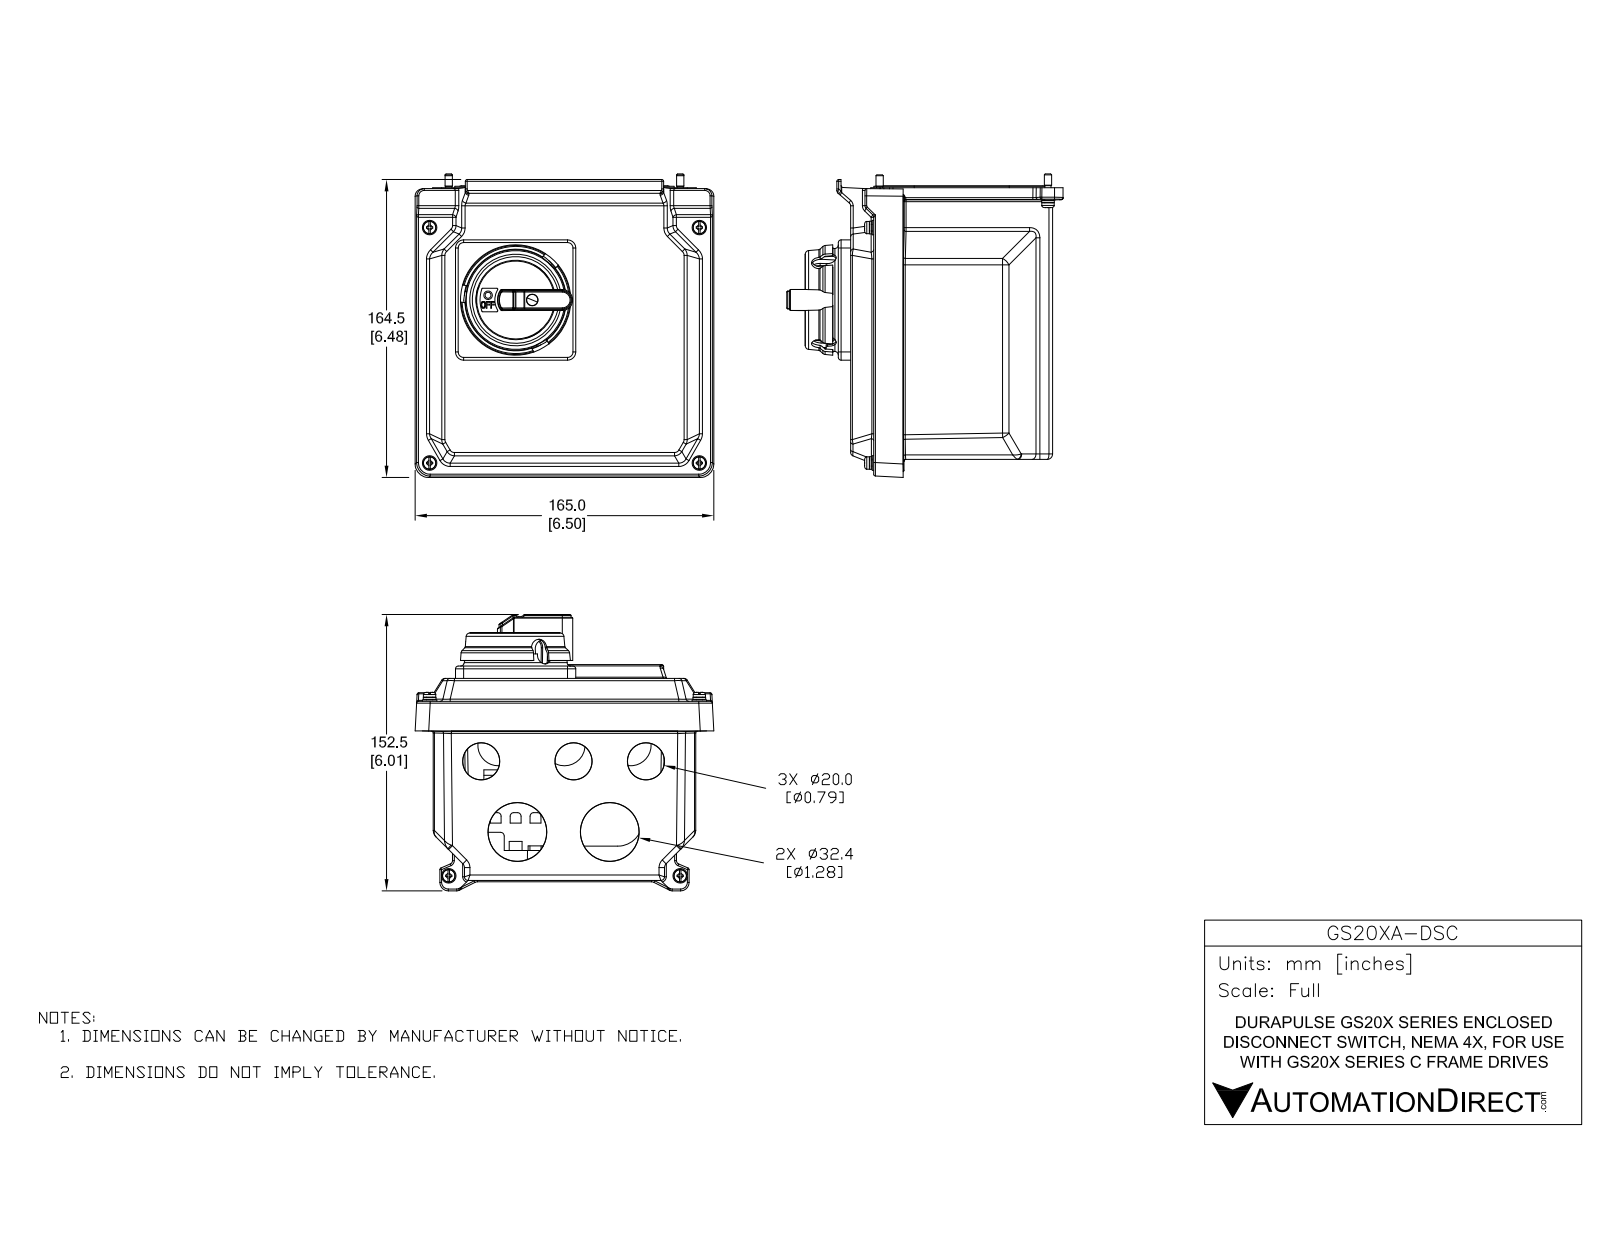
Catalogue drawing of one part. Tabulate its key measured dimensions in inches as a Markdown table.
| quantity | value |
| --- | --- |
| part name | GS20XA-DSC |
| STEP written by | SolidWorks 2017 (AUTOMOTIVE_DESIGN) |
| units | inches |
| bodies | 38 solids, 2365 faces (913 planar, 773 cylindrical, 679 other) |
| overall size | 6.598 × 6.496 × 6.01 |
| volume | 20.39 in³ |
| surface area | 438.3 in² |
| round holes (diameter × count) | 0.138 × 8, 0.142 × 8, 0.189 × 4, 0.22 × 4, 0.221 × 4, 0.226 × 4, 0.25 × 3, 0.591 × 3, 0.807 × 3, 1.28 × 2, 0.128 × 1, 0.185 × 1 |
| round bosses / shafts (diameter × count) | 0.276 × 8, 0.268 × 8, 0.157 × 8, 0.134 × 8, 0.315 × 6, 0.988 × 3, 0.929 × 3, 0.78 × 3 |
| partial cylindrical surfaces (radius × count) | 0.02 × 105, 0.039 × 67, 0.079 × 50, 0.197 × 28, 0.012 × 27, 0.098 × 19, 0.118 × 14, 0.004 × 11 |
| main face-to-face distances | 0.098, 4.285, 4.384, 4.187, 3.785, 0.5, 5.748, 0.315, 0.02, 0.925 |
| hole center spacings | 1.336, 1.89, 1.726, 1.11, 1.613, 2.008, 2.672, 3.189 |
